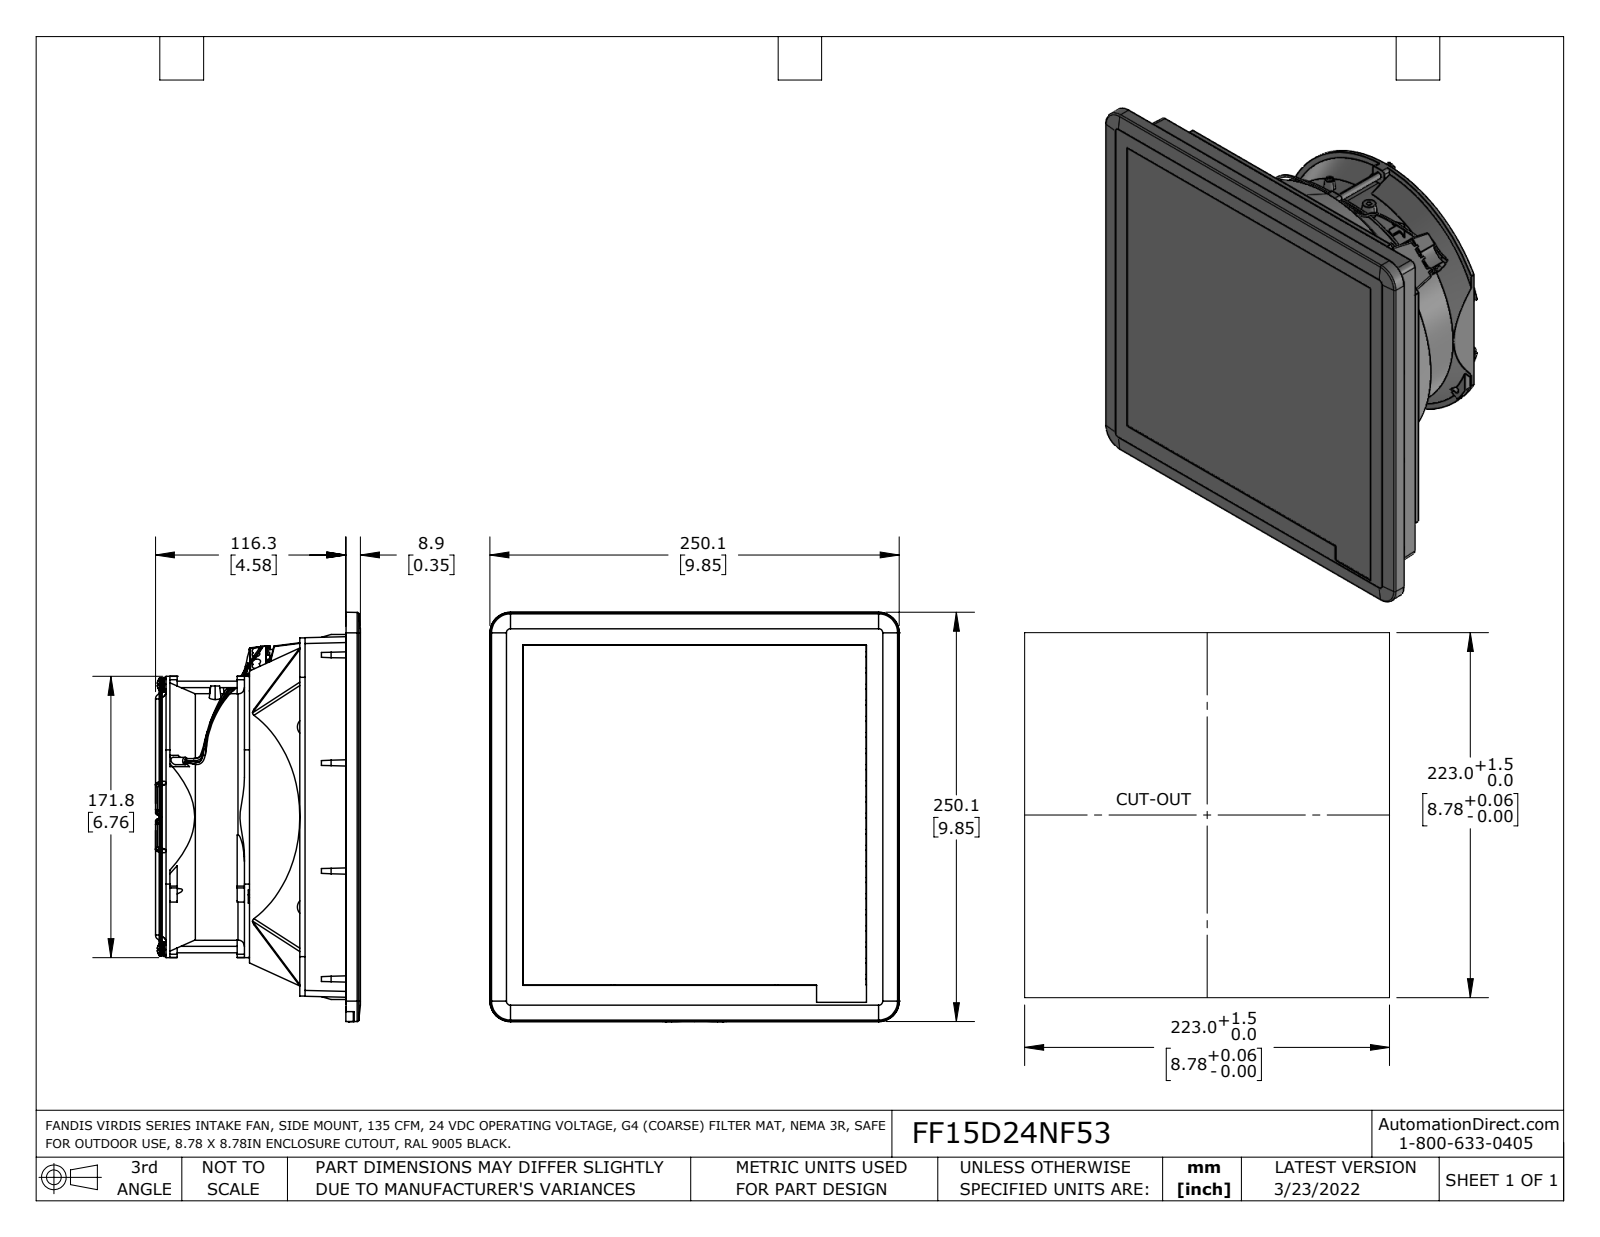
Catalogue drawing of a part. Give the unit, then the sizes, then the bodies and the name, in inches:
Units: inches
Overall size (bounding box): 9.847 × 9.847 × 4.931
Round holes (diameter × count): ⌀0.171 ×4, ⌀0.126 ×1
Round bosses / shafts (diameter × count): ⌀0.091 ×5, ⌀0.315 ×2, ⌀0.157 ×2, ⌀0.13 ×2, ⌀5.929 ×1
Partial cylindrical surfaces — rounded edges, fillets, slot ends (radius × count): R0.012 ×33, R0.02 ×17, R0.016 ×15, R0.079 ×12, R0.028 ×11, R0.039 ×11, R0.051 ×8, R0.177 ×8
Main face-to-face distances: 4.657, 0.331, 4.327, 0.35, 0.02, 4.677, 1.457, 1.437, 1.106, 3.22
Hole centre spacings: 2.97, 5.644, 5.256, 6.378
Volume: 233.6 in³ · Surface area: 369.3 in²
Bodies: 5 solids, 1218 faces (543 planar, 290 cylindrical, 385 other)
Part name (STEP PRODUCT): FF15DxxyF (p.c.)
STEP written by: SolidWorks 2021 (AUTOMOTIVE_DESIGN)
